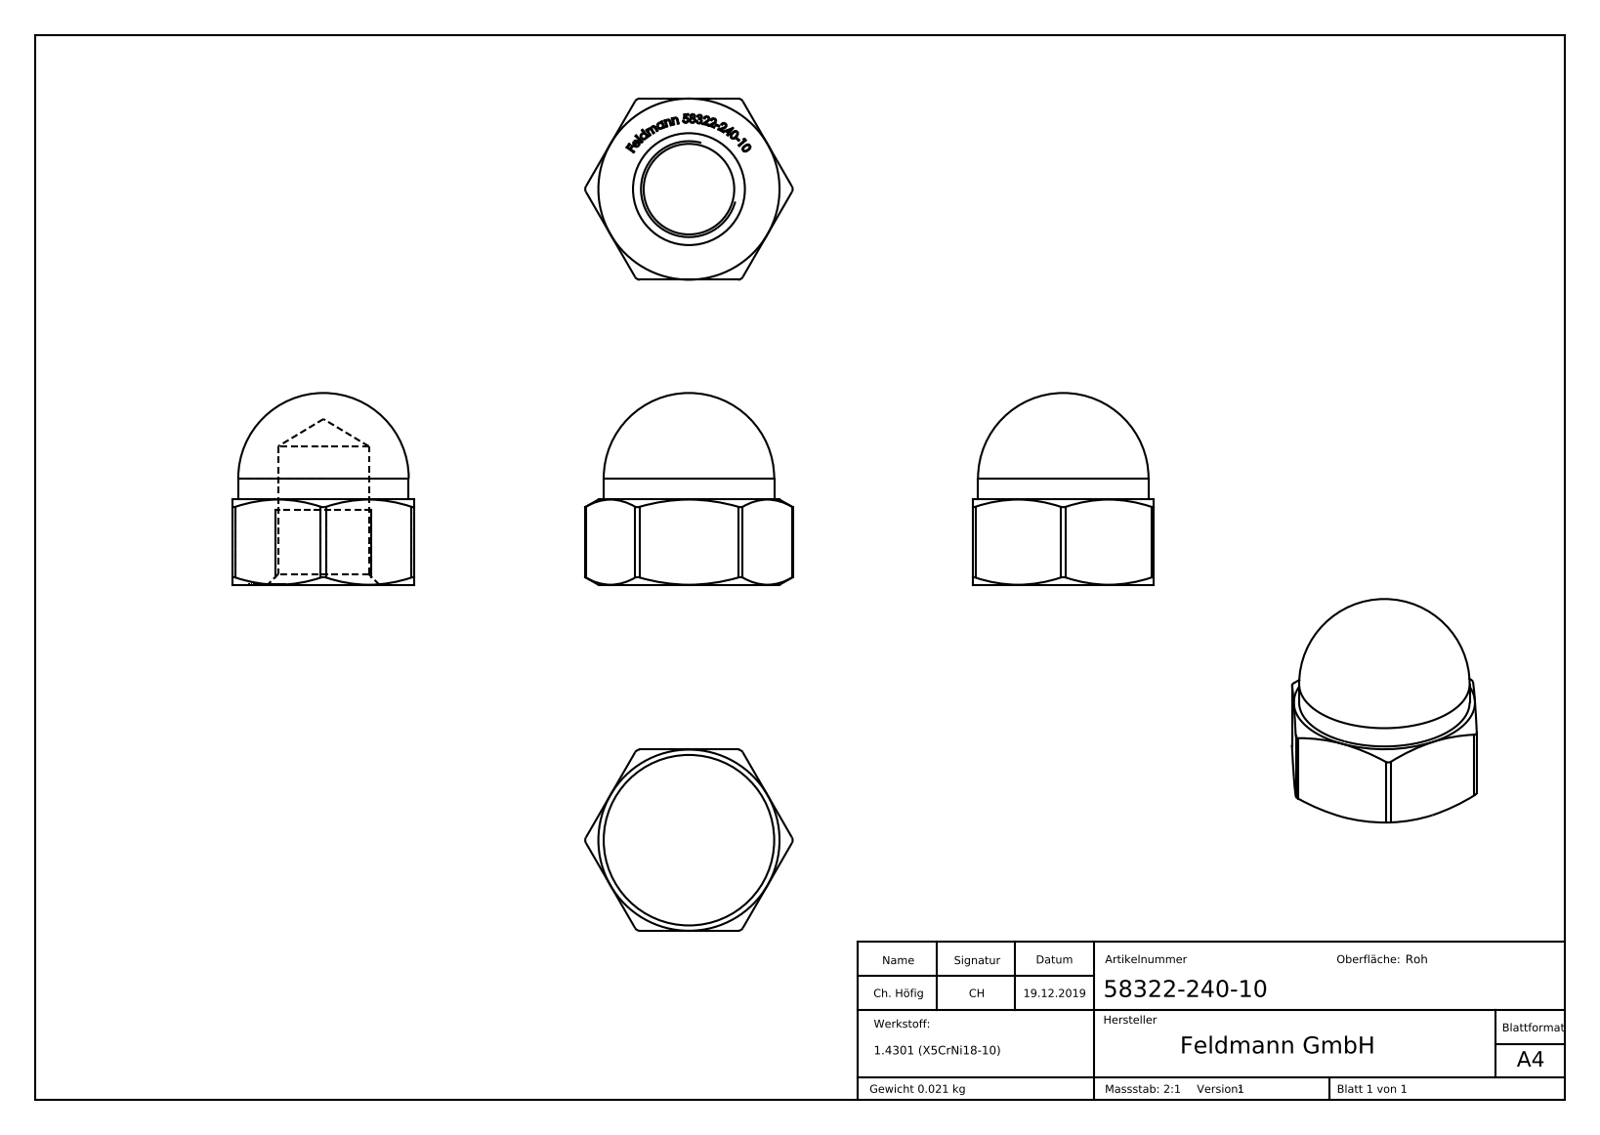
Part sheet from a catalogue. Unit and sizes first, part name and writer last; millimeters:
Units: millimetres
Overall size (bounding box): 23 × 19.48 × 17
Round holes (diameter × count): ⌀8.5 ×1
Round bosses / shafts (diameter × count): ⌀16 ×1
Partial cylindrical surfaces — rounded edges, fillets, slot ends (radius × count): R0.5 ×6
Main face-to-face distances: 17, 8
Volume: 2 665 mm³ · Surface area: 1 590 mm²
Bodies: 1 solid, 31 faces (8 planar, 8 cylindrical, 15 other)
Part name (STEP PRODUCT): 58322-240-10
STEP written by: SolidWorks 2015 (CONFIG_CONTROL_DESIGN)
